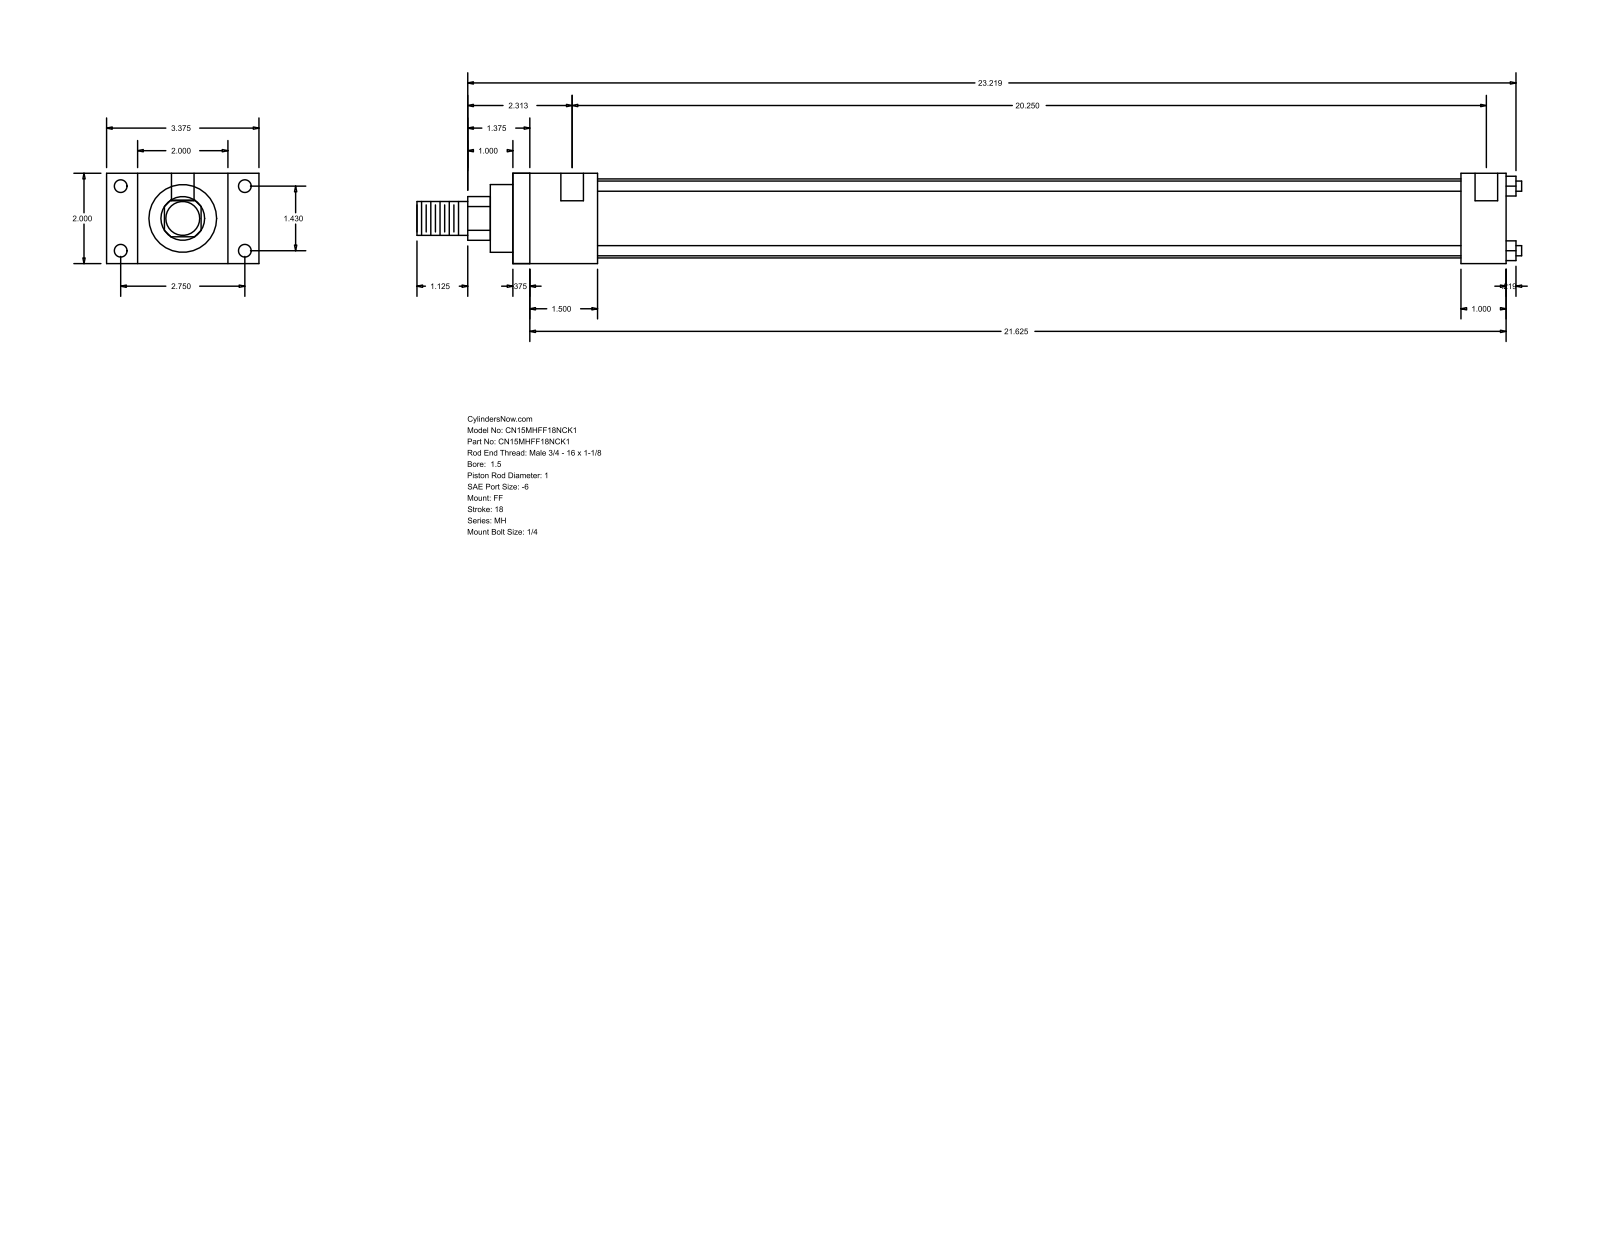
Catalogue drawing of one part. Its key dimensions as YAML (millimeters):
part_name: "MH_FF__0150_1"
step_written_by: "GSSL Pune (CONFIG_CONTROL_DESIGN)"
units: millimeters
bodies: {solids: 0, faces: 92, planar: 64, cylindrical: 28, other: 0}
overall_size: [621.51, 85.72, 50.8]
round_holes:
  - {diameter: 5.56, count: 4}
  - {diameter: 7.14, count: 4}
  - {diameter: 12.7, count: 2}
round_bosses_or_shafts:
  - {diameter: 5.71, count: 4}
  - {diameter: 44.45, count: 1}
  - {diameter: 38.1, count: 1}
  - {diameter: 25.4, count: 1}
  - {diameter: 19.05, count: 1}
partial_cylinders:
  - {radius: 12.29, count: 1}
face_to_face_distances: [50.8, 558.8, 9.52, 549.28, 25.4, 17.46, 68.26, 47.63, 38.11, 511.17]
hole_center_spacings: [36.32, 69.84, 78.72, 517.53, 3.18, 514.35]
